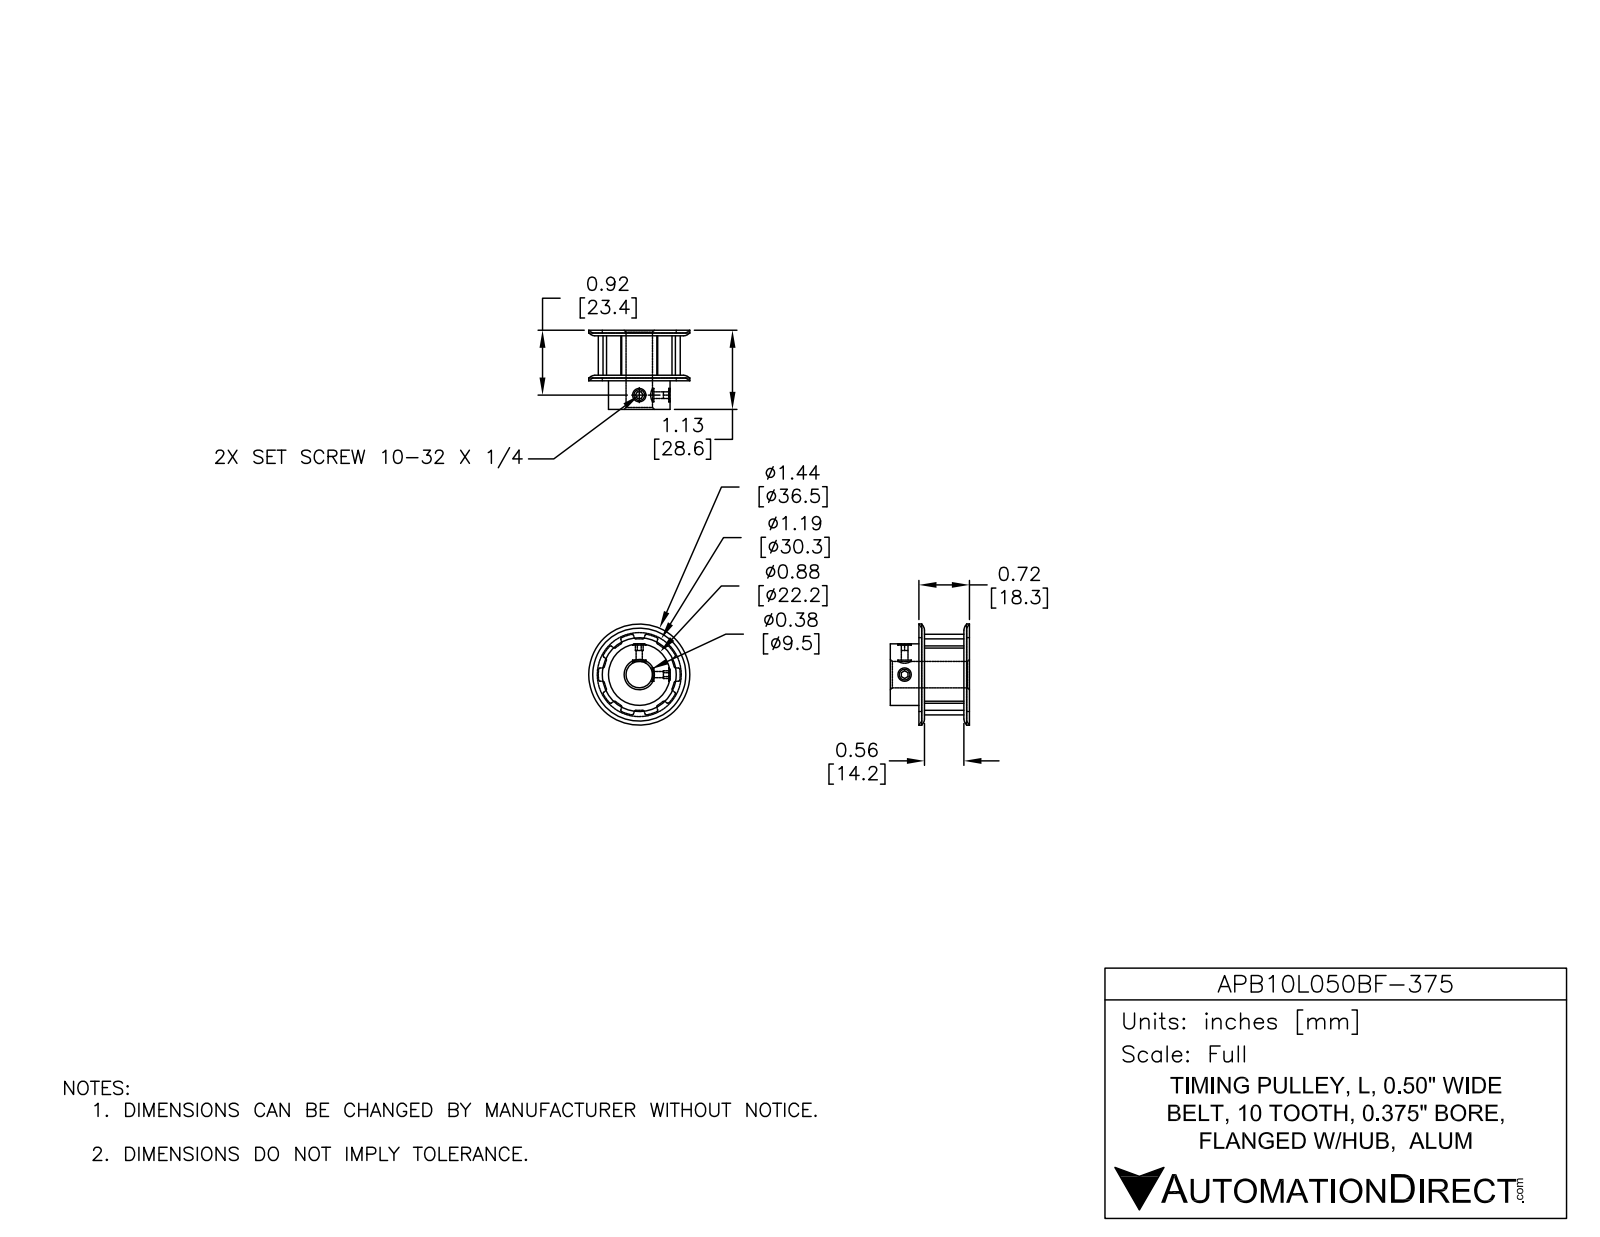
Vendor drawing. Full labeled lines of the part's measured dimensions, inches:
Part name (STEP PRODUCT): APB10L050BF-375
STEP written by: SolidWorks 2014 (AUTOMOTIVE_DESIGN)
Units: inches
Bodies: 1 solid, 102 faces (36 planar, 44 cylindrical, 22 other)
Overall size (bounding box): 1.438 × 1.438 × 1.125
Volume: 0.874 in³ · Surface area: 9.783 in²
Round holes (diameter × count): ⌀0.088 ×2, ⌀0.375 ×1
Round bosses / shafts (diameter × count): ⌀0.875 ×1
Partial cylindrical surfaces — rounded edges, fillets, slot ends (radius × count): R0.015 ×20, R0.527 ×1
Main face-to-face distances: 1.164, 0.64, 0.04, 0.68, 1.125, 1.085, 0.445, 0.402, 0.04, 0.6
